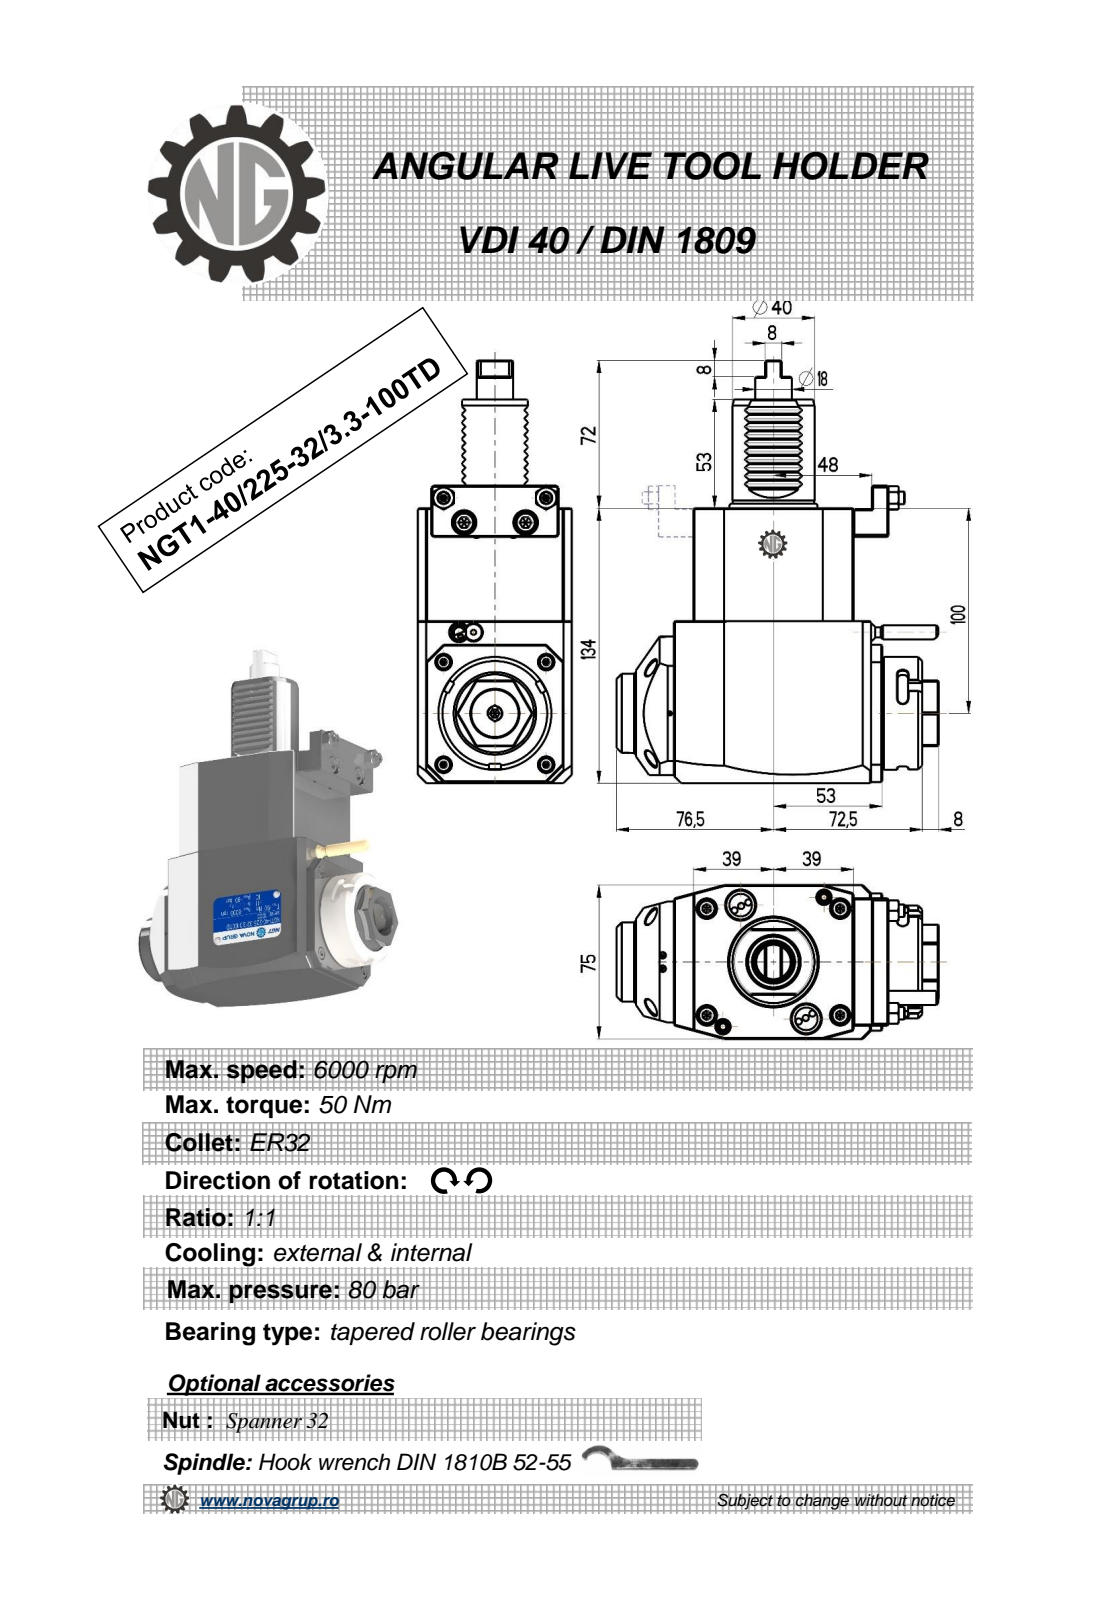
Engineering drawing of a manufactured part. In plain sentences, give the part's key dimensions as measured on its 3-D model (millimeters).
The part is named "NGT1_40_225_32_3_3_100TD". Its 3-D file was written by "PRO/ENGINEER BY PARAMETRIC TECHNOLOGY CORPORATION, 2010280 (CONFIG_CONTROL_DESIGN)". It is 1 solid with 426 faces: 229 planar, 89 cylindrical and 108 other. Overall it measures 206 by 157 by 75 millimeters. Its volume is 1 088 000 cubic millimeters and its surface area 79 650 square millimeters. Round holes: 2 of diameter 2, 2 of diameter 2.6, 1 of diameter 2.5, 1 of diameter 3, 1 of diameter 23. Round bosses or shafts: 2 of diameter 40, 2 of diameter 6, 1 of diameter 55, 1 of diameter 48, 1 of diameter 38.5, 1 of diameter 17.8, 1 of diameter 8, 1 of diameter 7. Partial cylindrical surfaces (rounded edges, fillets, slot ends): 20 of radius 0.3, 10 of radius 0.31, 6 of radius 0.2, 6 of radius 2.5, 2 of radius 0.8, 2 of radius 180, 1 of radius 24.5, 1 of radius 37.5. The main face-to-face distances are 75, 134, 14, 78, 0.5, 92, 8.5, 19.5, 84.88, 8. The hole center spacings are 14.25, 28.5, 39.63, 43.2, 50.68.
